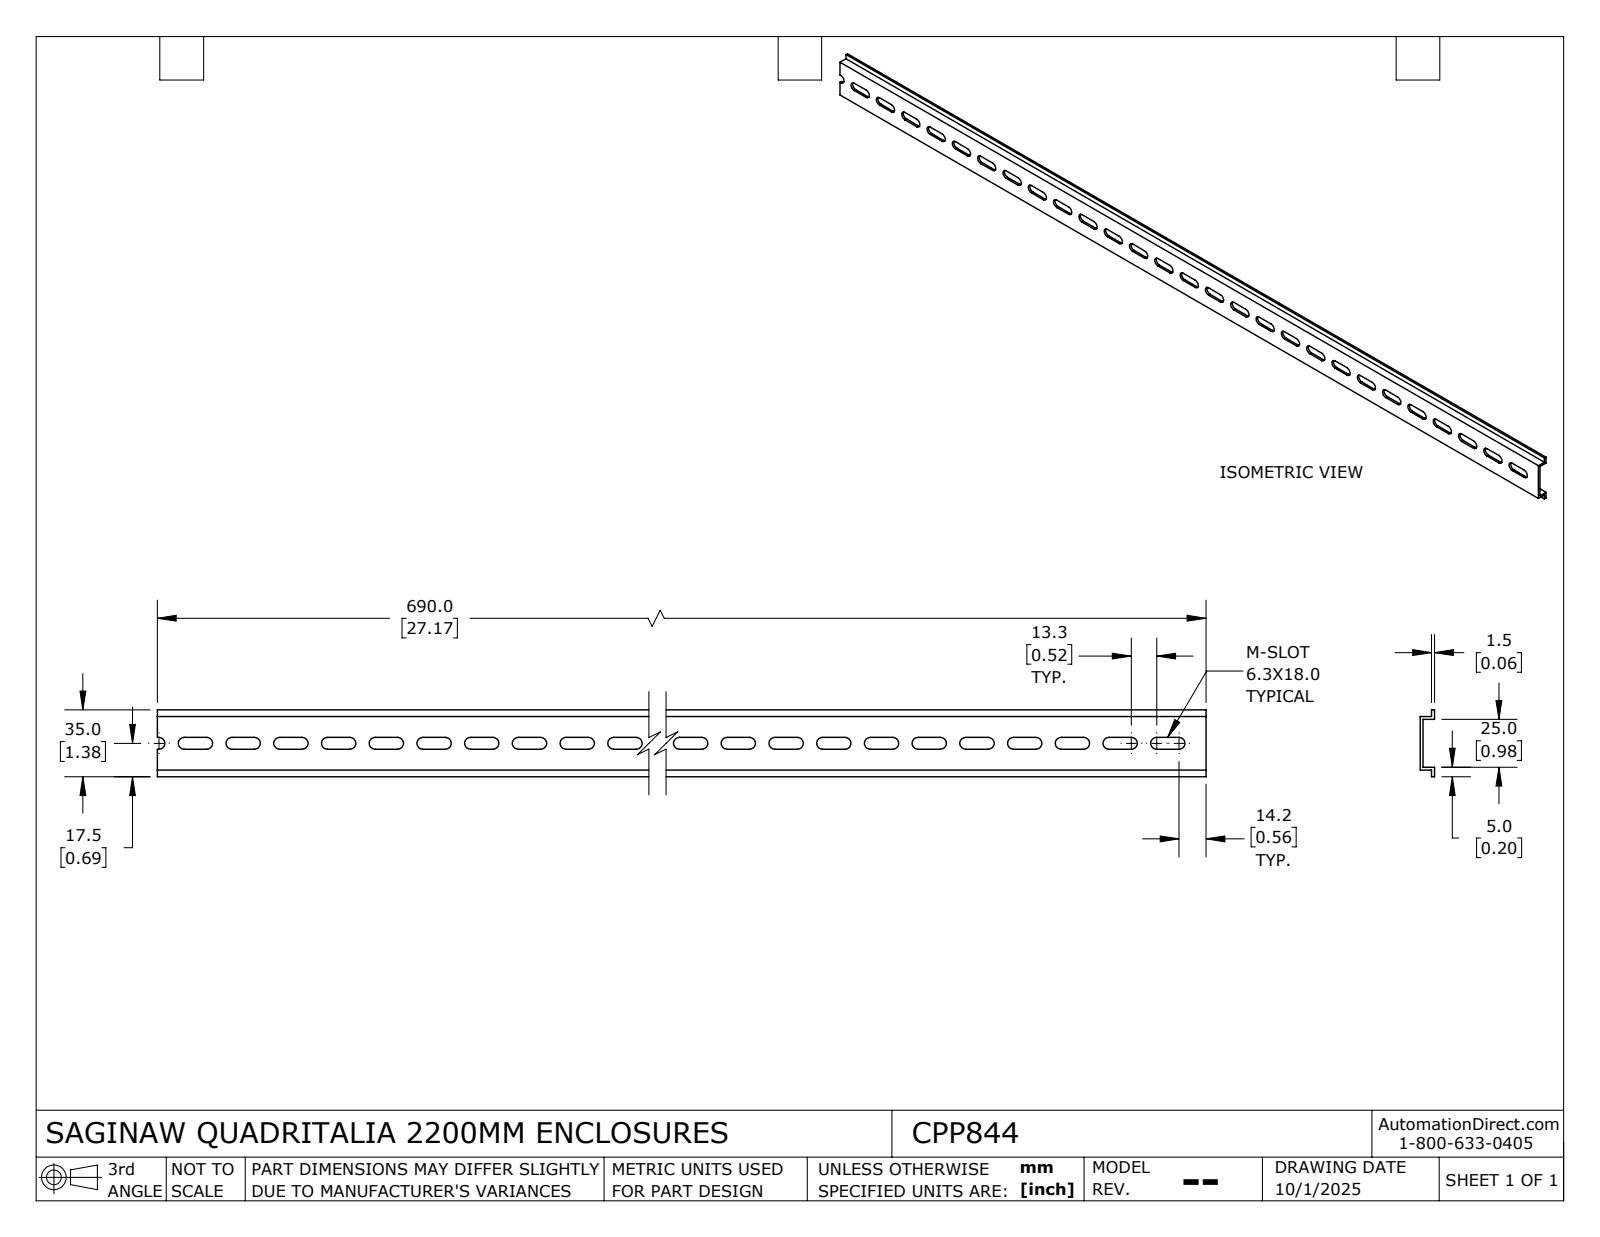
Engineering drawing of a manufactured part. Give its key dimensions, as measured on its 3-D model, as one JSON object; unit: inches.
{"part_name": "CPP844_Default", "step_written_by": "SolidWorks 2024 (CONFIG_CONTROL_DESIGN)", "units": "inches", "bodies": {"solids": 1, "faces": 126, "planar": 71, "cylindrical": 55, "other": 0}, "overall_size": [27.165, 1.378, 0.295], "volume_in3": 2.707, "surface_area_in2": 97.84, "partial_cylinders_radius": [[0.124, 55]], "face_to_face_distances": [0.059, 0.236, 1.043, 0.295, 0.177, 1.102, 0.984, 0.138, 0.197, 1.181]}
